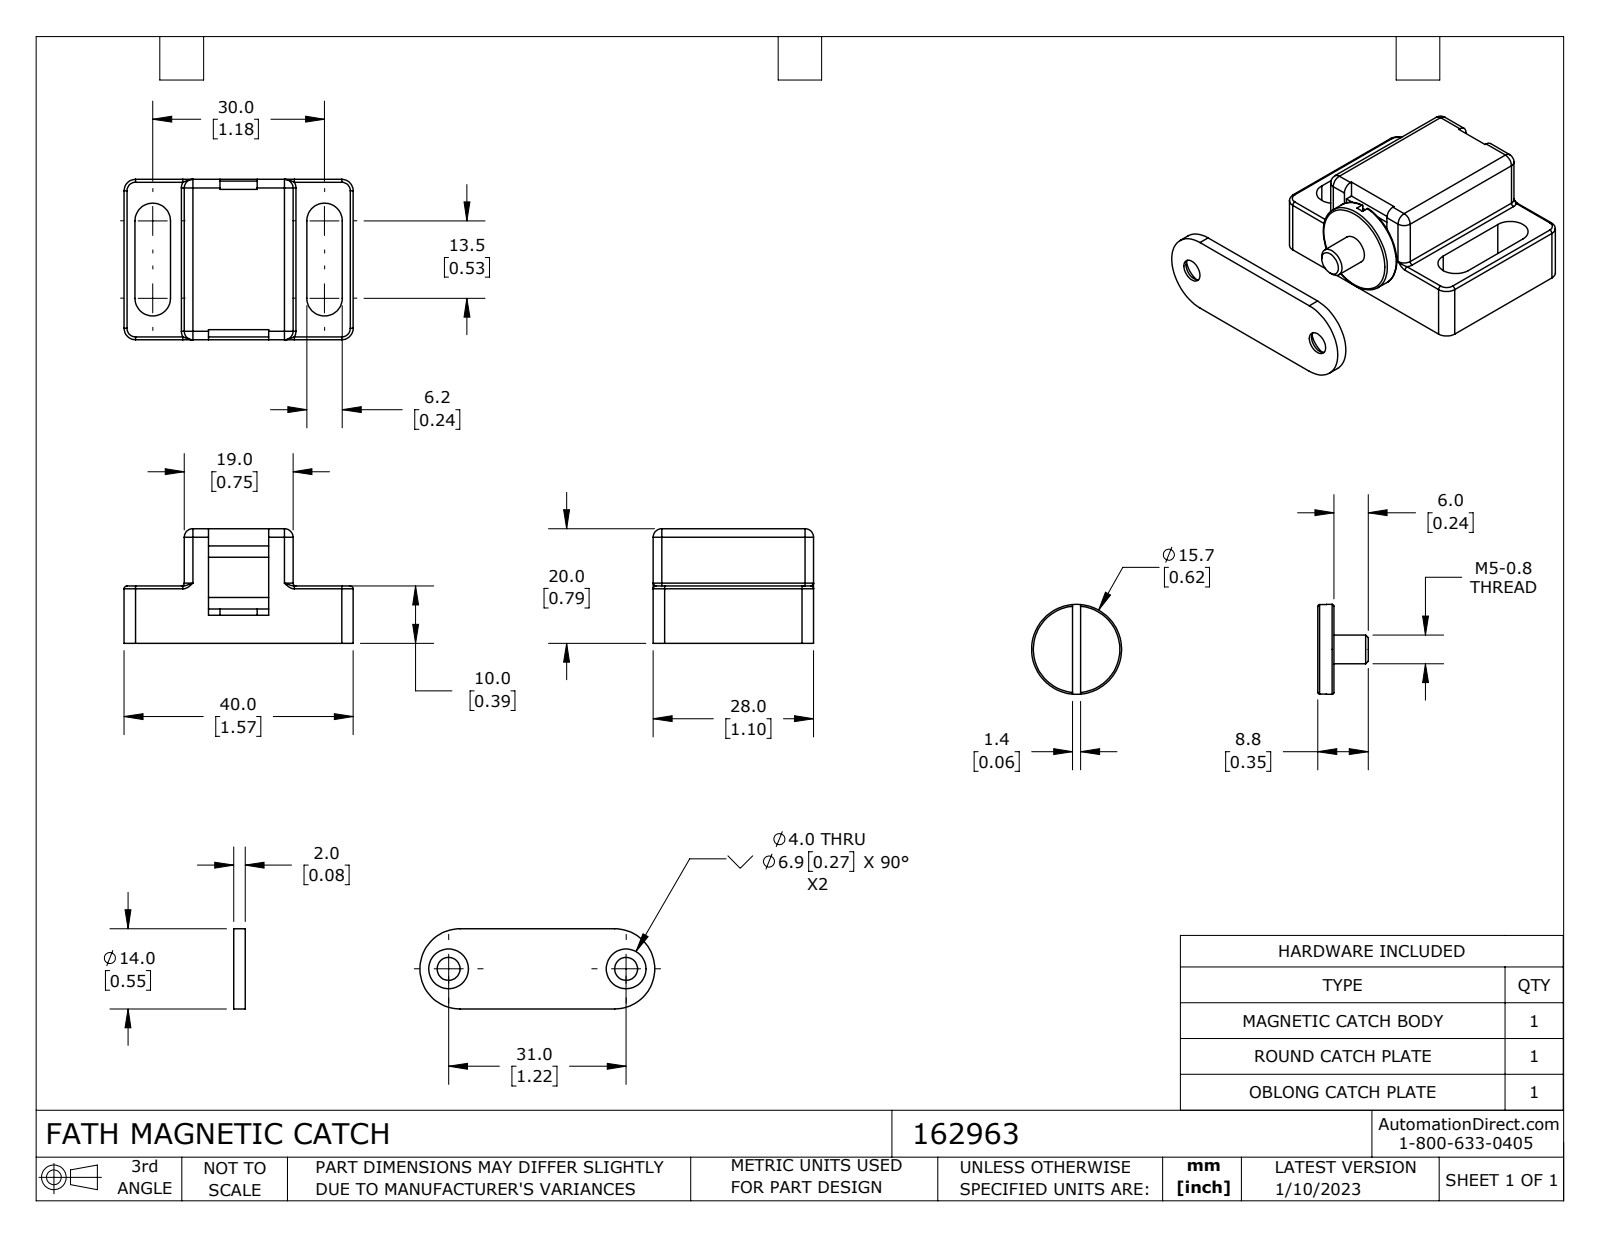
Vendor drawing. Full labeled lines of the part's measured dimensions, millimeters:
Part name (STEP PRODUCT): 162963_3; 162963_1; 162963_2; 162963
STEP written by: SolidWorks 2021 (CONFIG_CONTROL_DESIGN)
Units: millimetres
Bodies: 6 solids, 148 faces (72 planar, 47 cylindrical, 29 other)
Overall size (bounding box): 55.4 × 41 × 20
Volume: 12 800 mm³ · Surface area: 10 610 mm²
Round holes (diameter × count): ⌀4 ×2
Round bosses / shafts (diameter × count): ⌀15.7 ×1, ⌀5 ×1
Partial cylindrical surfaces — rounded edges, fillets, slot ends (radius × count): R1.5 ×8, R0.5 ×6, R1 ×4, R2 ×4, R3.1 ×4, R7 ×2
Main face-to-face distances: 2, 9, 7, 14, 5, 0.5, 10, 2.3, 8, 15
Hole centre spacings: 31
